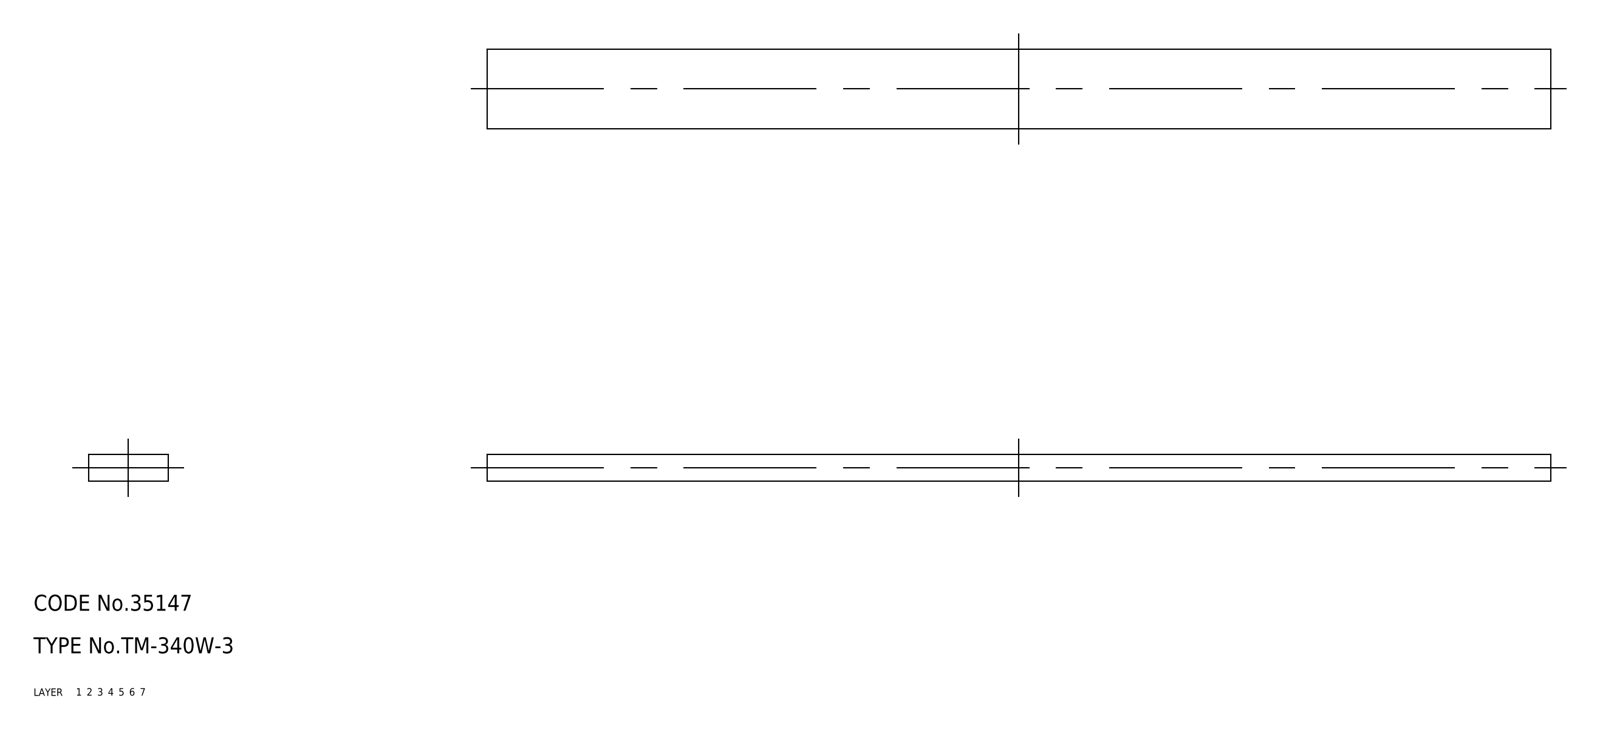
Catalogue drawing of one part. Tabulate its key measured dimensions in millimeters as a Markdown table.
| quantity | value |
| --- | --- |
| part name | TM_340W_3; rubber foam |
| STEP written by | SolidWorks 2015 (AUTOMOTIVE_DESIGN) |
| units | millimeters |
| bodies | 1 solid, 6 faces (6 planar, 0 cylindrical, 0 other) |
| overall size | 200 × 15 × 5 |
| volume | 15 000 mm³ |
| surface area | 8 150 mm² |
| main face-to-face distances | 5, 15, 200 |
